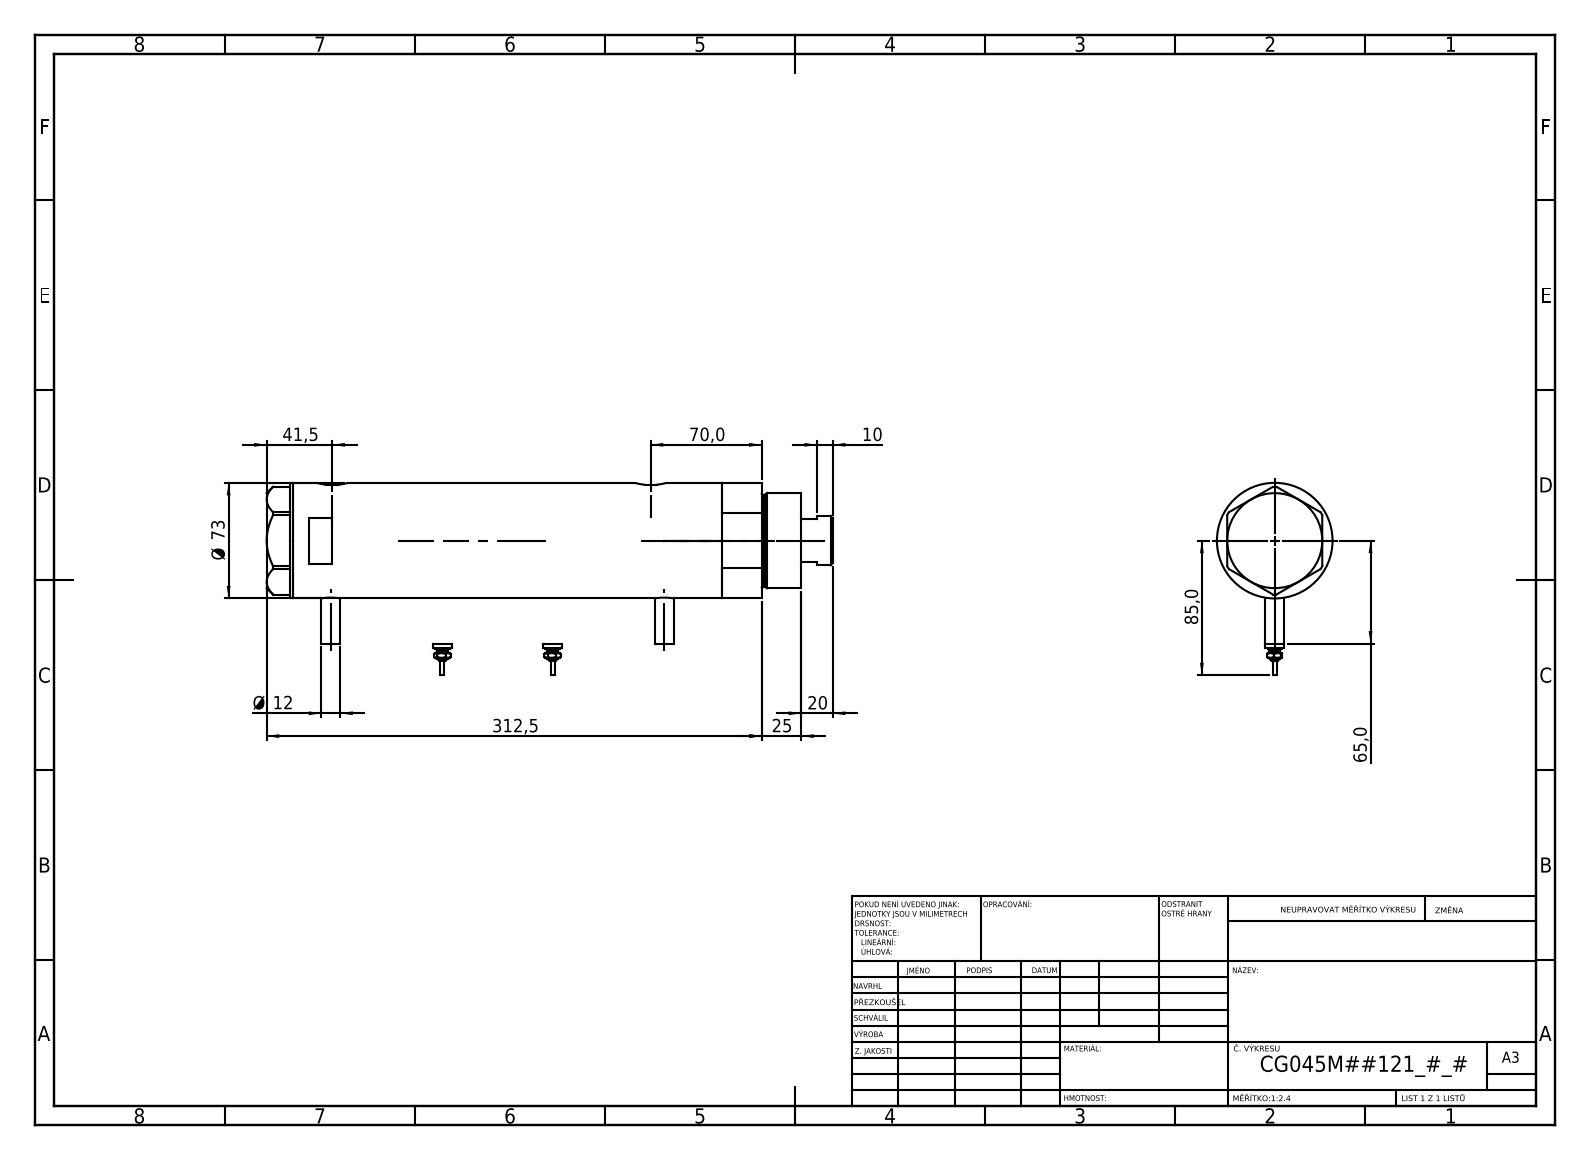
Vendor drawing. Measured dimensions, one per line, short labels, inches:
name: V270CG_BACK; V270CG_VC; Switch; V270CG_MIDDLE (+1 more)
written by: SolidWorks 2019 (CONFIG_CONTROL_DESIGN)
unit: in
bodies: 6 solids, 212 faces (77 planar, 71 cylindrical, 64 other)
size: 14.075 × 4.783 × 2.874
volume: 77.87 in³; area: 314 in²
holes: 2× ⌀0.492, 2× ⌀0.518, 1× ⌀0.413, 1× ⌀1.26, 1× ⌀1.319, 1× ⌀1.772, 1× ⌀1.89, 1× ⌀2.52
bosses: 4× ⌀0.472, 2× ⌀0.354, 2× ⌀0.276, 2× ⌀0.177, 2× ⌀0.098, 1× ⌀2.874, 1× ⌀2.362, 1× ⌀2.283
rounds: 2× R0.394
face distances: 8.898, 1.024, 7.874, 0.65, 1.673, 9.547, 0.079, 12.638, 3.74, 13.287
hole spacings: 0.039, 0.335, 7.913, 7.953, 8.248, 8.287
